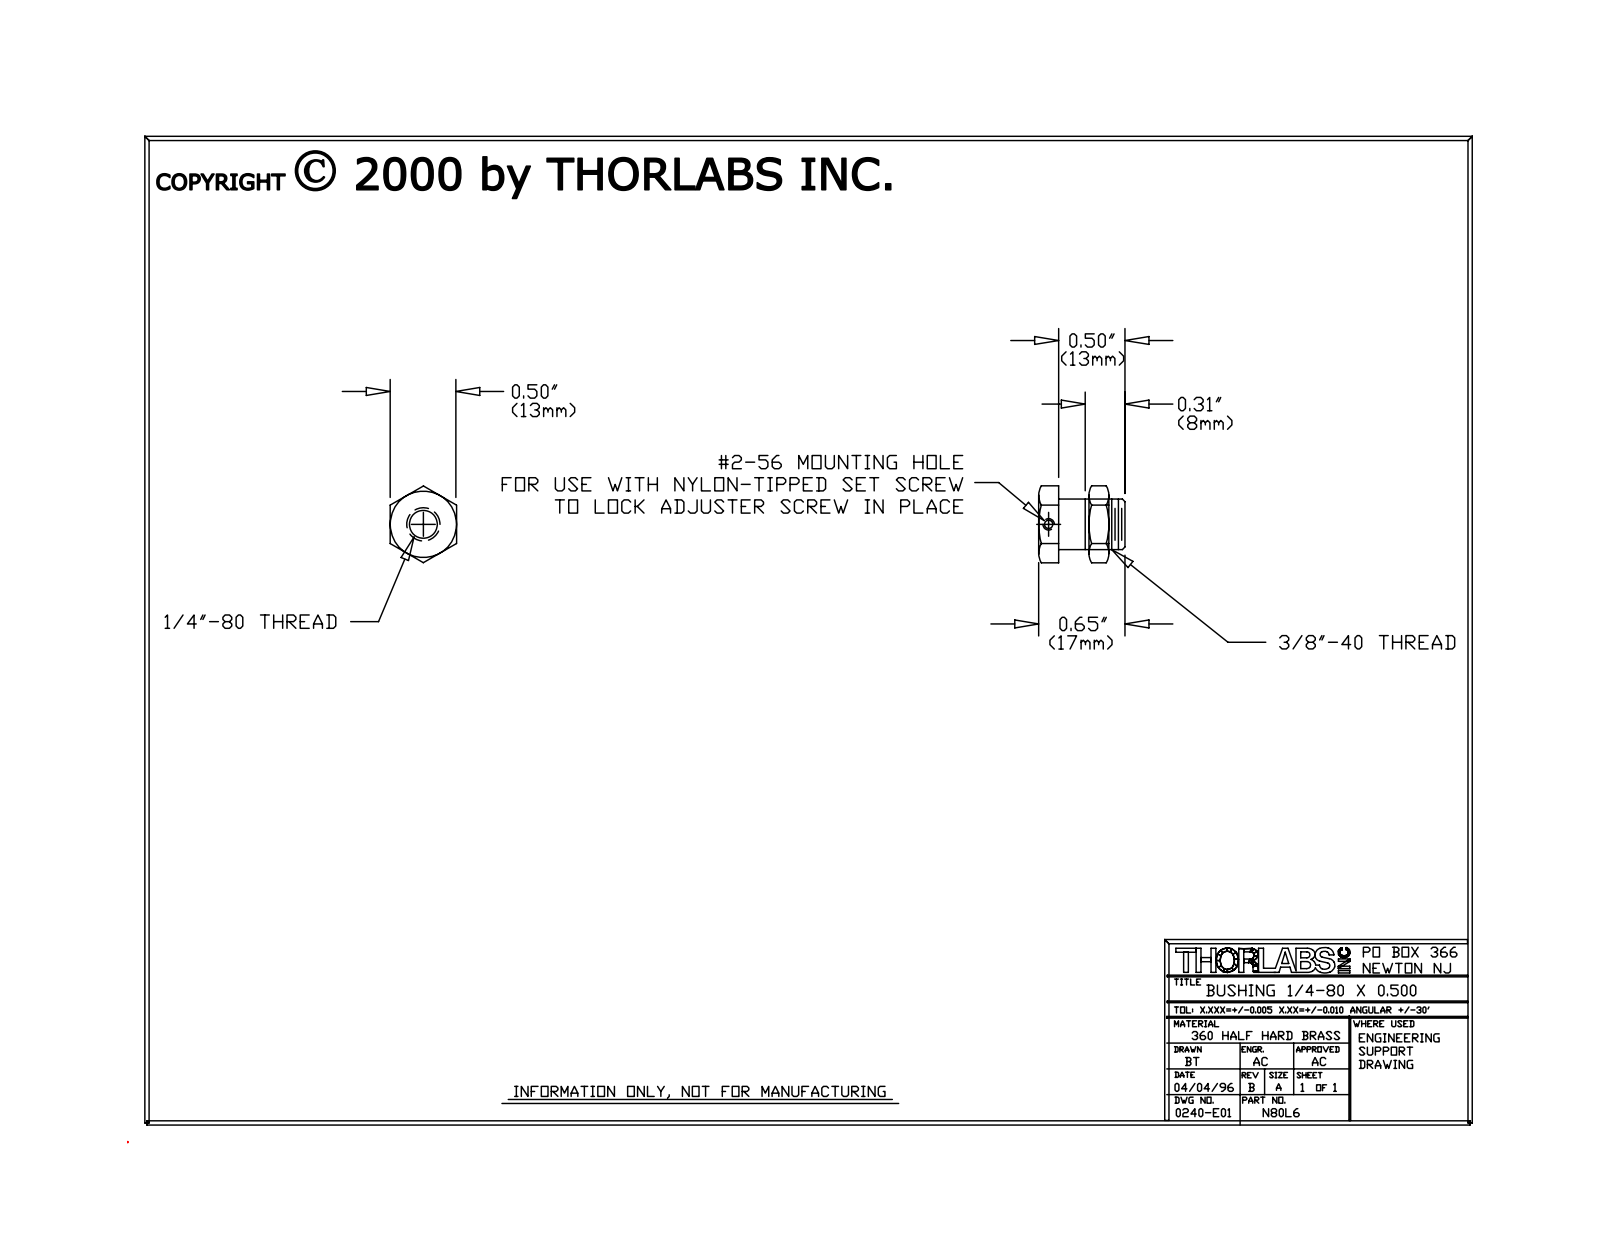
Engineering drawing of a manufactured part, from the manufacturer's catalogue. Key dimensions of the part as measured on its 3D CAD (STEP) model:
Part name (STEP PRODUCT): 0240-E0W
STEP written by: SolidWorks 2007 (AUTOMOTIVE_DESIGN)
Units: inches
Bodies: 3 solids, 65 faces (27 planar, 14 cylindrical, 24 other)
Overall size (bounding box): 0.65 × 0.577 × 0.5
Volume: 0.079 in³ · Surface area: 2.298 in²
Round holes (diameter × count): ⌀0.086 ×1, ⌀0.21 ×1, ⌀0.345 ×1
Round bosses / shafts (diameter × count): ⌀0.374 ×1, ⌀0.35 ×1, ⌀0.057 ×1
Main face-to-face distances: 0.5, 0.15, 0.125, 0.319, 0.469, 0.194, 0.344, 0.181, 0.306, 0.65
